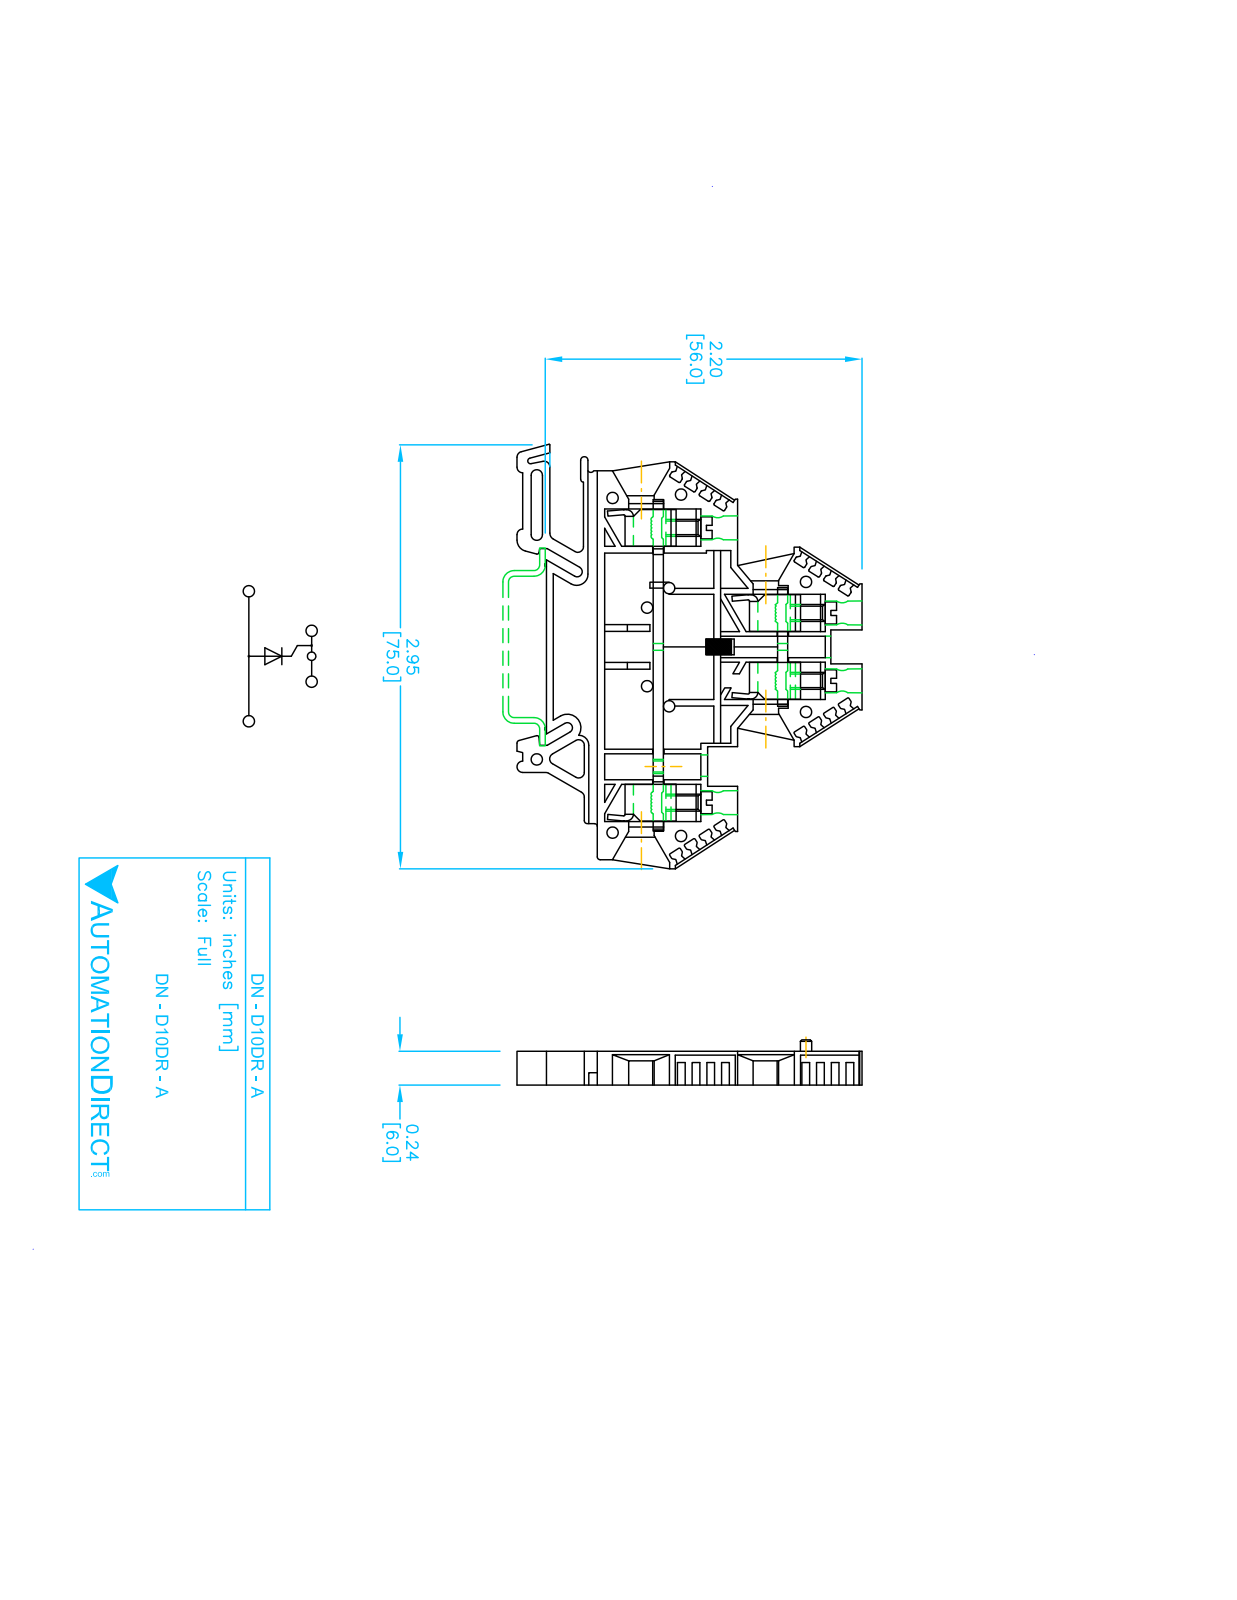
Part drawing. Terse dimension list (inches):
name: DN-D10DR-A
written by: SolidWorks 2017 (AUTOMOTIVE_DESIGN)
unit: in
bodies: 1 solid, 402 faces (261 planar, 141 cylindrical, 0 other)
size: 2.957 × 2.402 × 0.236
volume: 0.9 in³; area: 14.85 in²
holes: 4× ⌀0.165, 1× ⌀0.079
bosses: 4× ⌀0.146
rounds: 64× R0.008, 13× R0.039, 6× R0.02, 2× R0.012, 2× R0.035, 2× R0.075, 2× R0.079, 1× R0.004
face distances: 0.236, 0.079, 0.157, 0.354, 0.059, 0.024, 0.031, 0.047, 0.976, 0.071
hole spacings: 0.472, 0.593, 0.848, 1.065, 1.321, 1.913
